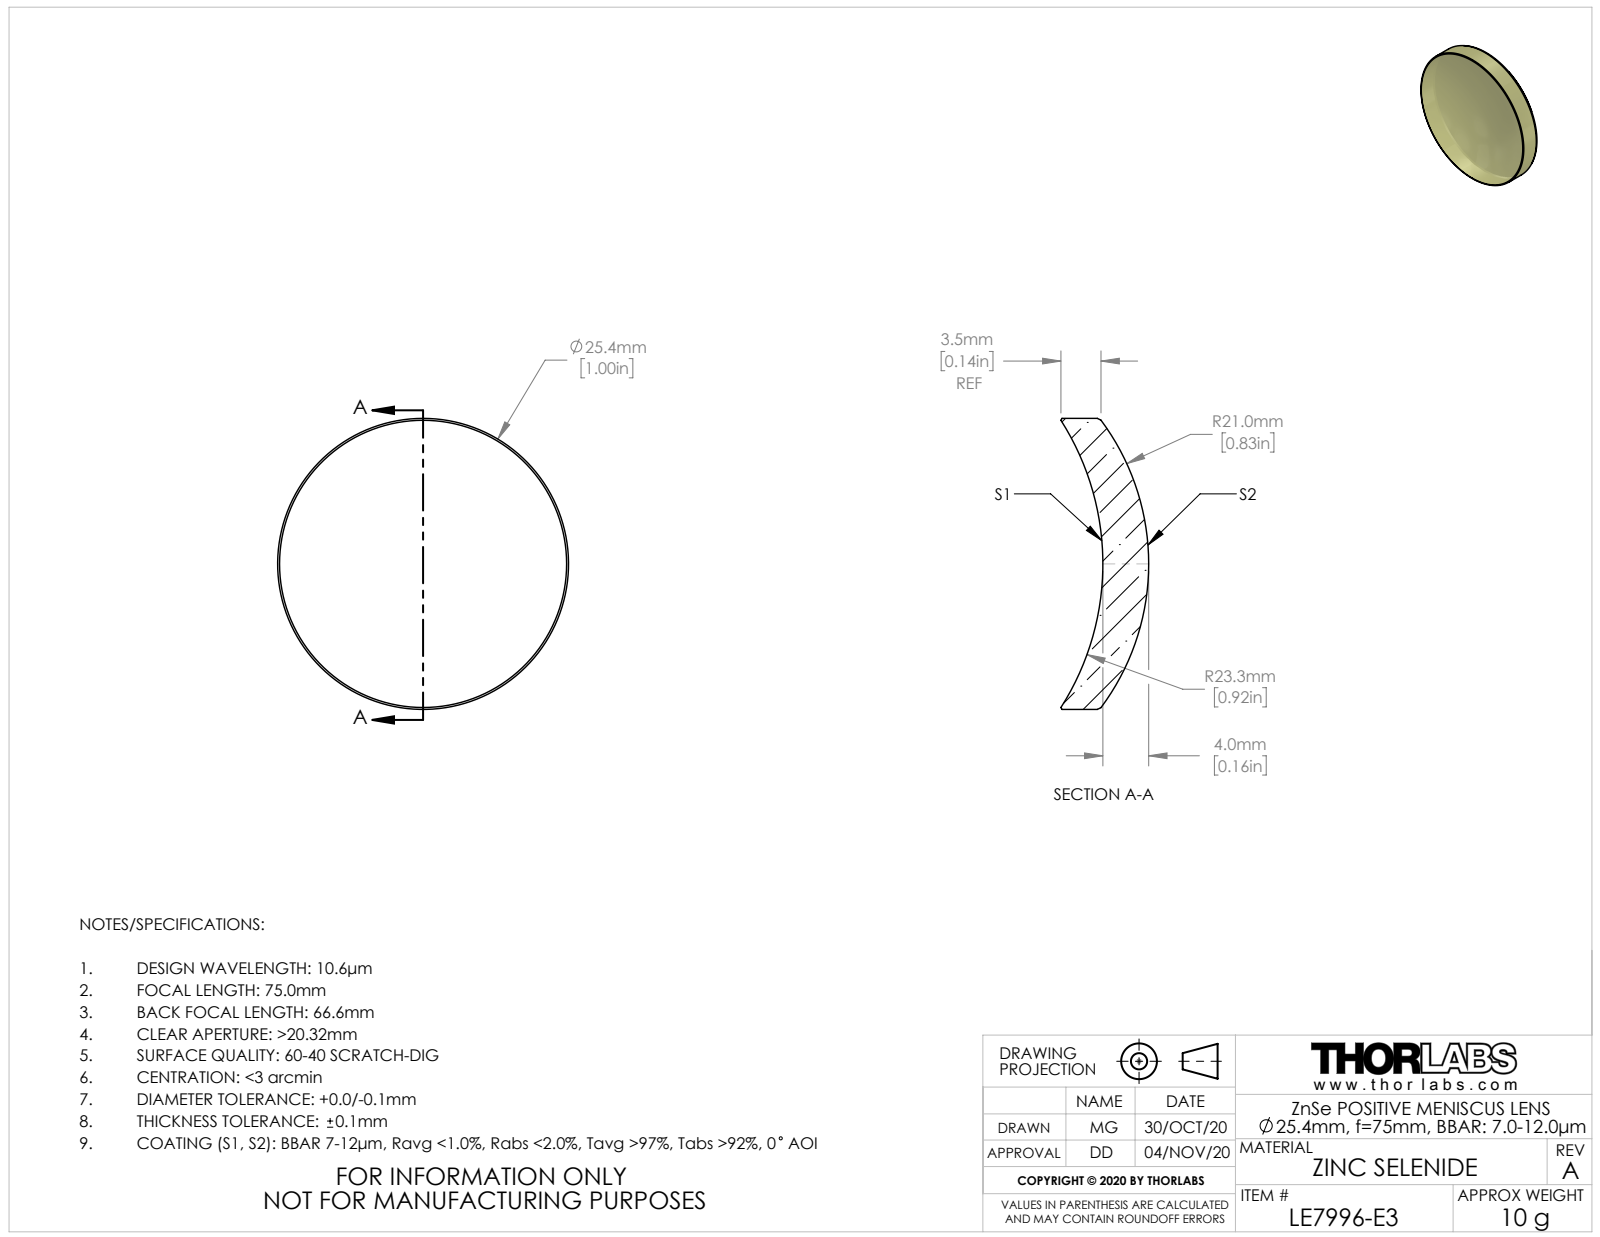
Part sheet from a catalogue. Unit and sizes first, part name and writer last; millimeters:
Units: millimetres
Overall size (bounding box): 25.4 × 25.4 × 7.66
Round bosses / shafts (diameter × count): ⌀25.4 ×1
Volume: 1 907 mm³ · Surface area: 1 374 mm²
Bodies: 1 solid, 10 faces (0 planar, 2 cylindrical, 8 other)
Part name (STEP PRODUCT): TTN225629-E0W
STEP written by: SolidWorks 2018 (CONFIG_CONTROL_DESIGN)
